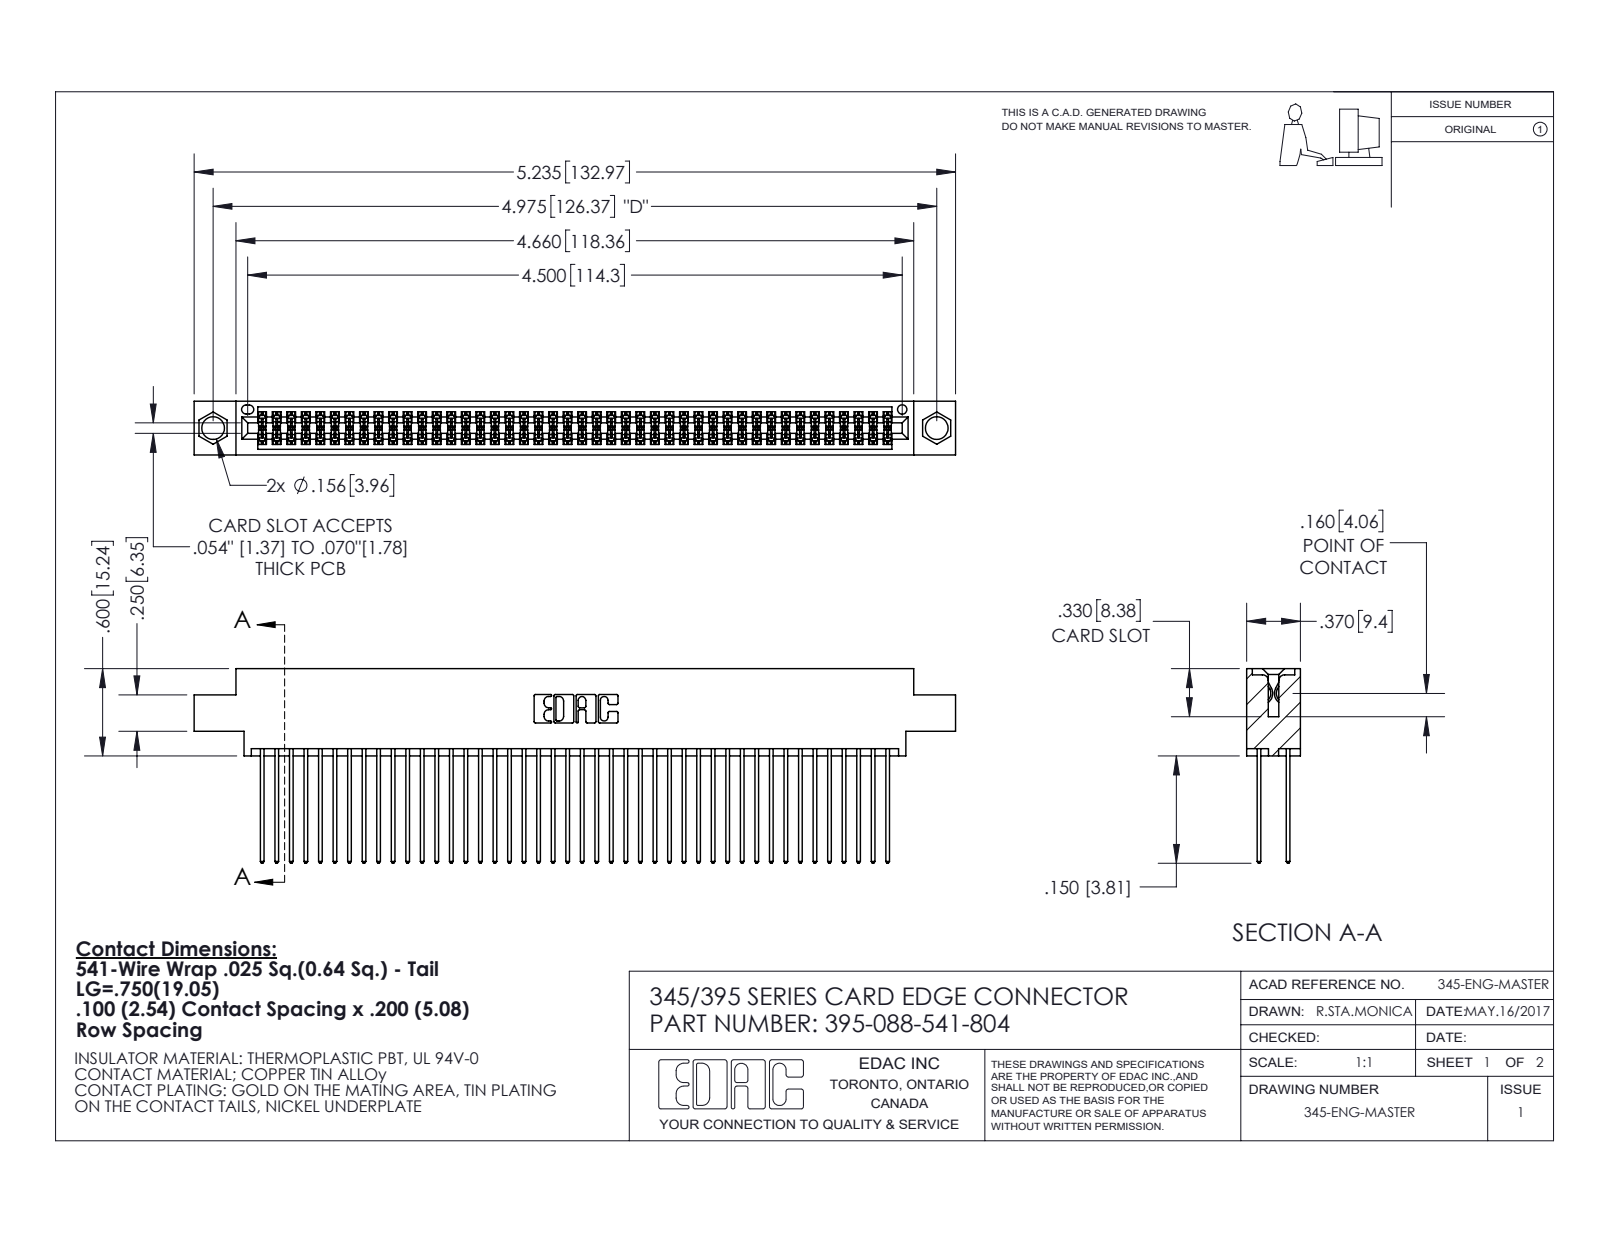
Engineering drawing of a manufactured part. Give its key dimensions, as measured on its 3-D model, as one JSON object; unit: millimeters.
{"part_name": "395-088-541-804; 345-292-001_345-293-141; 345 Part_0.170 Offset - 0.156 Dia-TI", "step_written_by": "SolidWorks 2020 (CONFIG_CONTROL_DESIGN)", "units": "millimeters", "bodies": {"solids": 89, "faces": 4544, "planar": 3002, "cylindrical": 1542, "other": 0}, "overall_size": [133, 34, 9.4], "volume_mm3": 13200, "surface_area_mm2": 21950, "round_holes": [[4, 2], [1.6, 1]], "partial_cylinders_radius": [[0.2, 132], [0.3, 88], [0.3, 22], [0.2, 6], [0.8, 6], [0.7, 3], [0.4, 2], [0.5, 2]], "face_to_face_distances": [1.8, 7.6, 5.1, 2.5, 6.9, 0.6, 5.7, 9.4, 4.4, 3.8], "hole_center_spacings": [6.9, 120.4, 126.4]}
